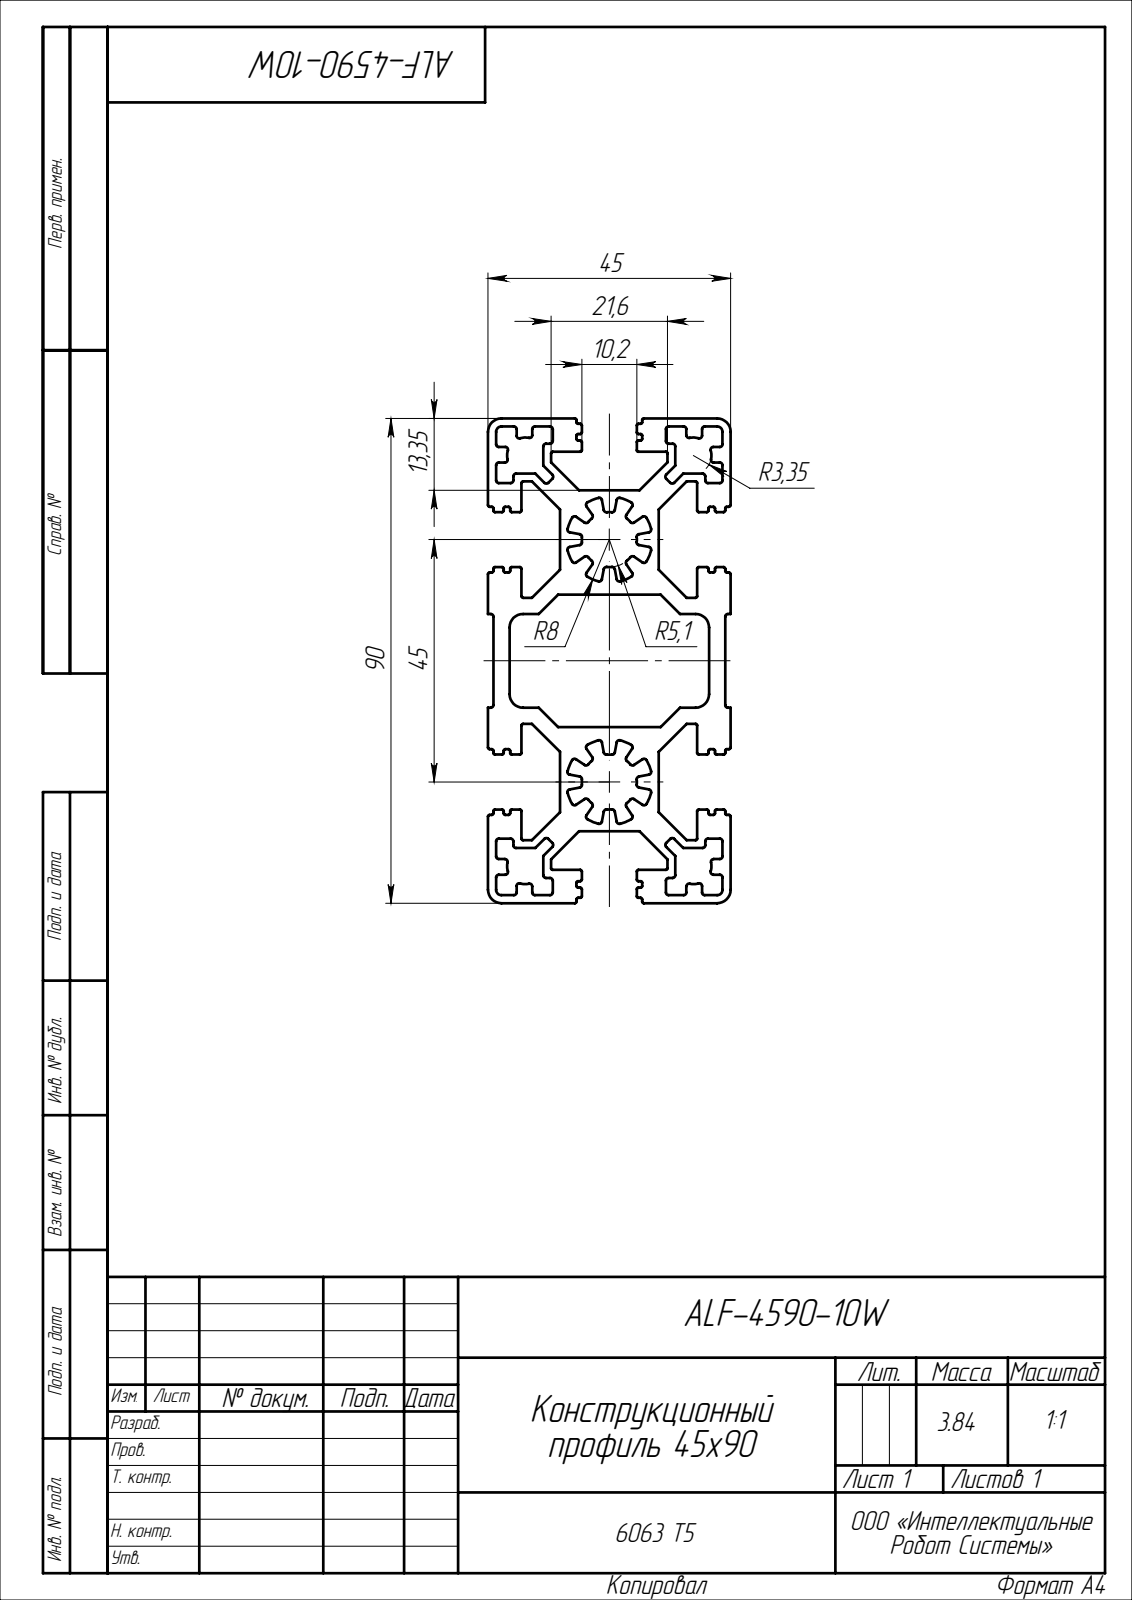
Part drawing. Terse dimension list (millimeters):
name: ALF-4590-10W
written by: SolidWorks 2022 (CONFIG_CONTROL_DESIGN)
unit: mm
bodies: 1 solid, 586 faces (258 planar, 328 cylindrical, 0 other)
size: 1000 × 90 × 45
volume: 1 428 000 mm³; area: 1 023 000 mm²
rounds: 132× R0.5, 108× R0.3, 8× R2.5, 4× R1, 4× R3.35, 2× R5.1, 2× R8
face distances: 7.15, 13.35, 6.2, 45, 4.05, 31.65, 34.8, 38.8, 25.45, 1.5
